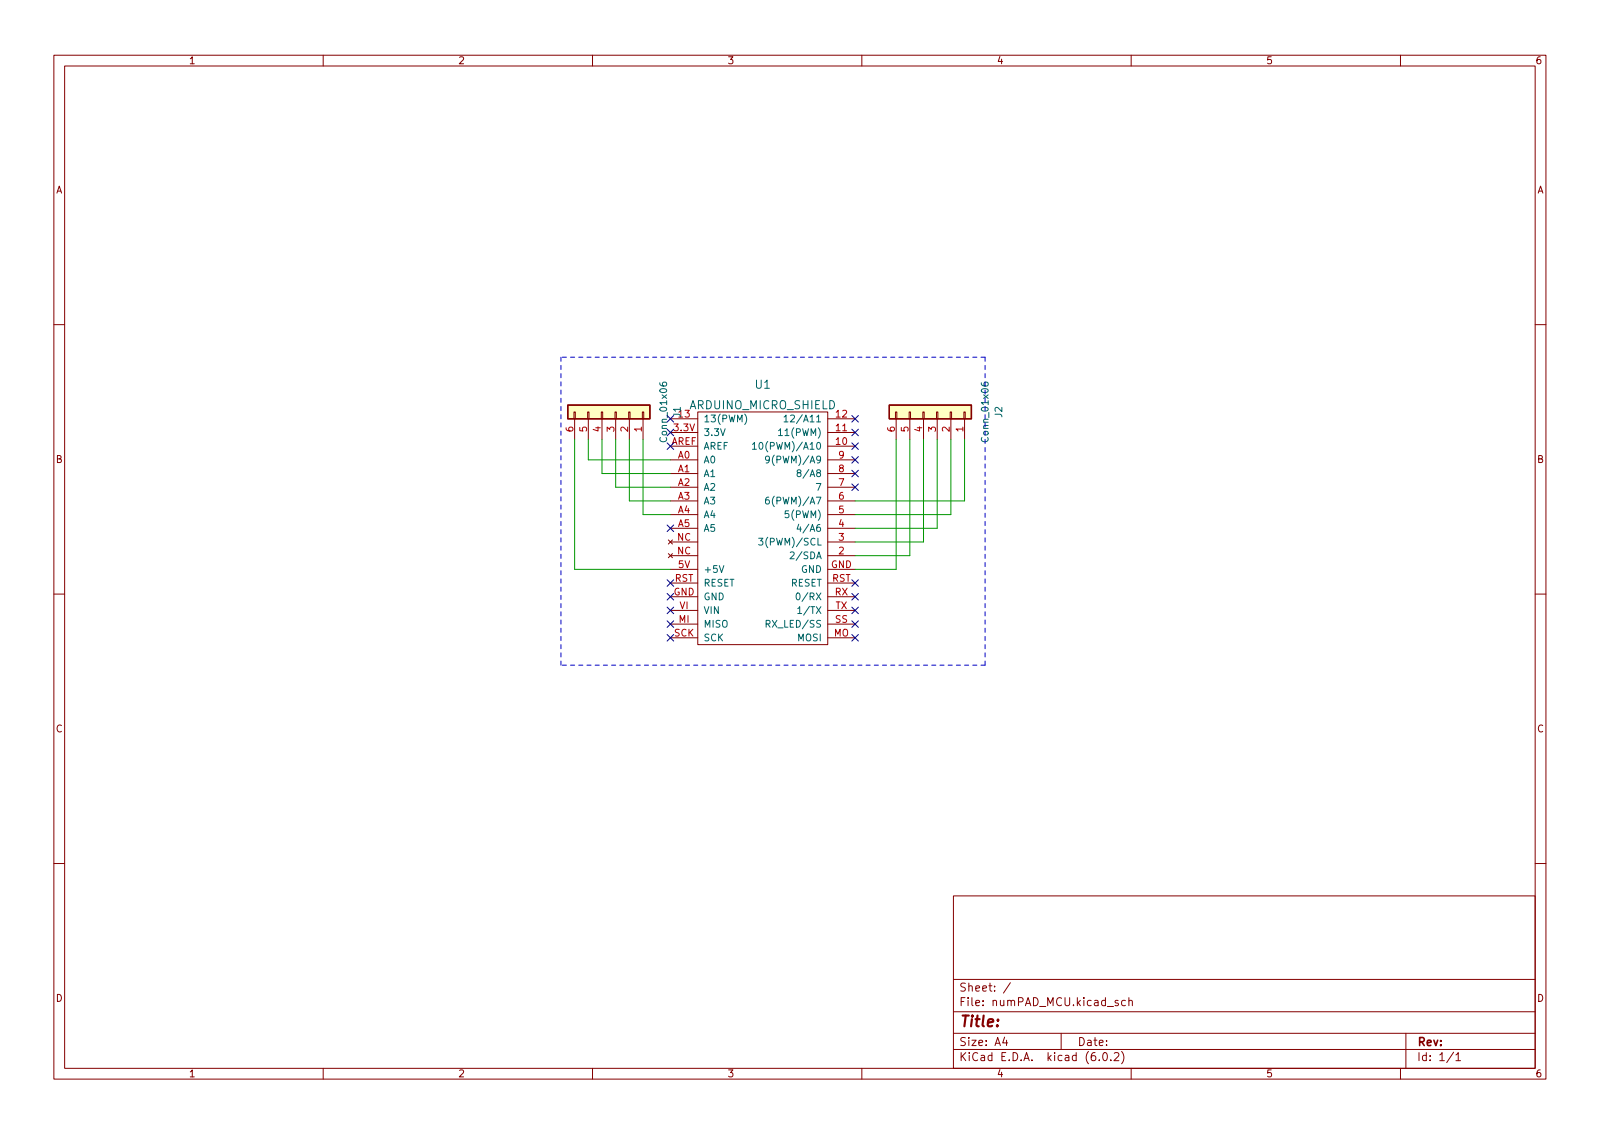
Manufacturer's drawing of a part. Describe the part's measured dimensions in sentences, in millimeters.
The part is named "numPAD_MCU 1; Pin Header 1x6 TH Pitch 2.54mm; COMPOUND; ARDUINO MICRO (+1 more)". Its 3-D file was written by "KiCad to STEP converter (AUTOMOTIVE_DESIGN)". It is 105 solids with 6557 faces: 8 planar, 46 cylindrical and 6503 other. Overall it measures 77 by 49.72 by 18.6 millimeters. Its volume is 6 709 cubic millimeters and its surface area 12 322 square millimeters. Round holes: 46 of diameter 1. The main face-to-face distances are 1.6, 48.5, 77. The hole center spacings are 2.54, 5.08, 7.62, 10.16, 15.47, 16.08, 12.7, 17.06.
